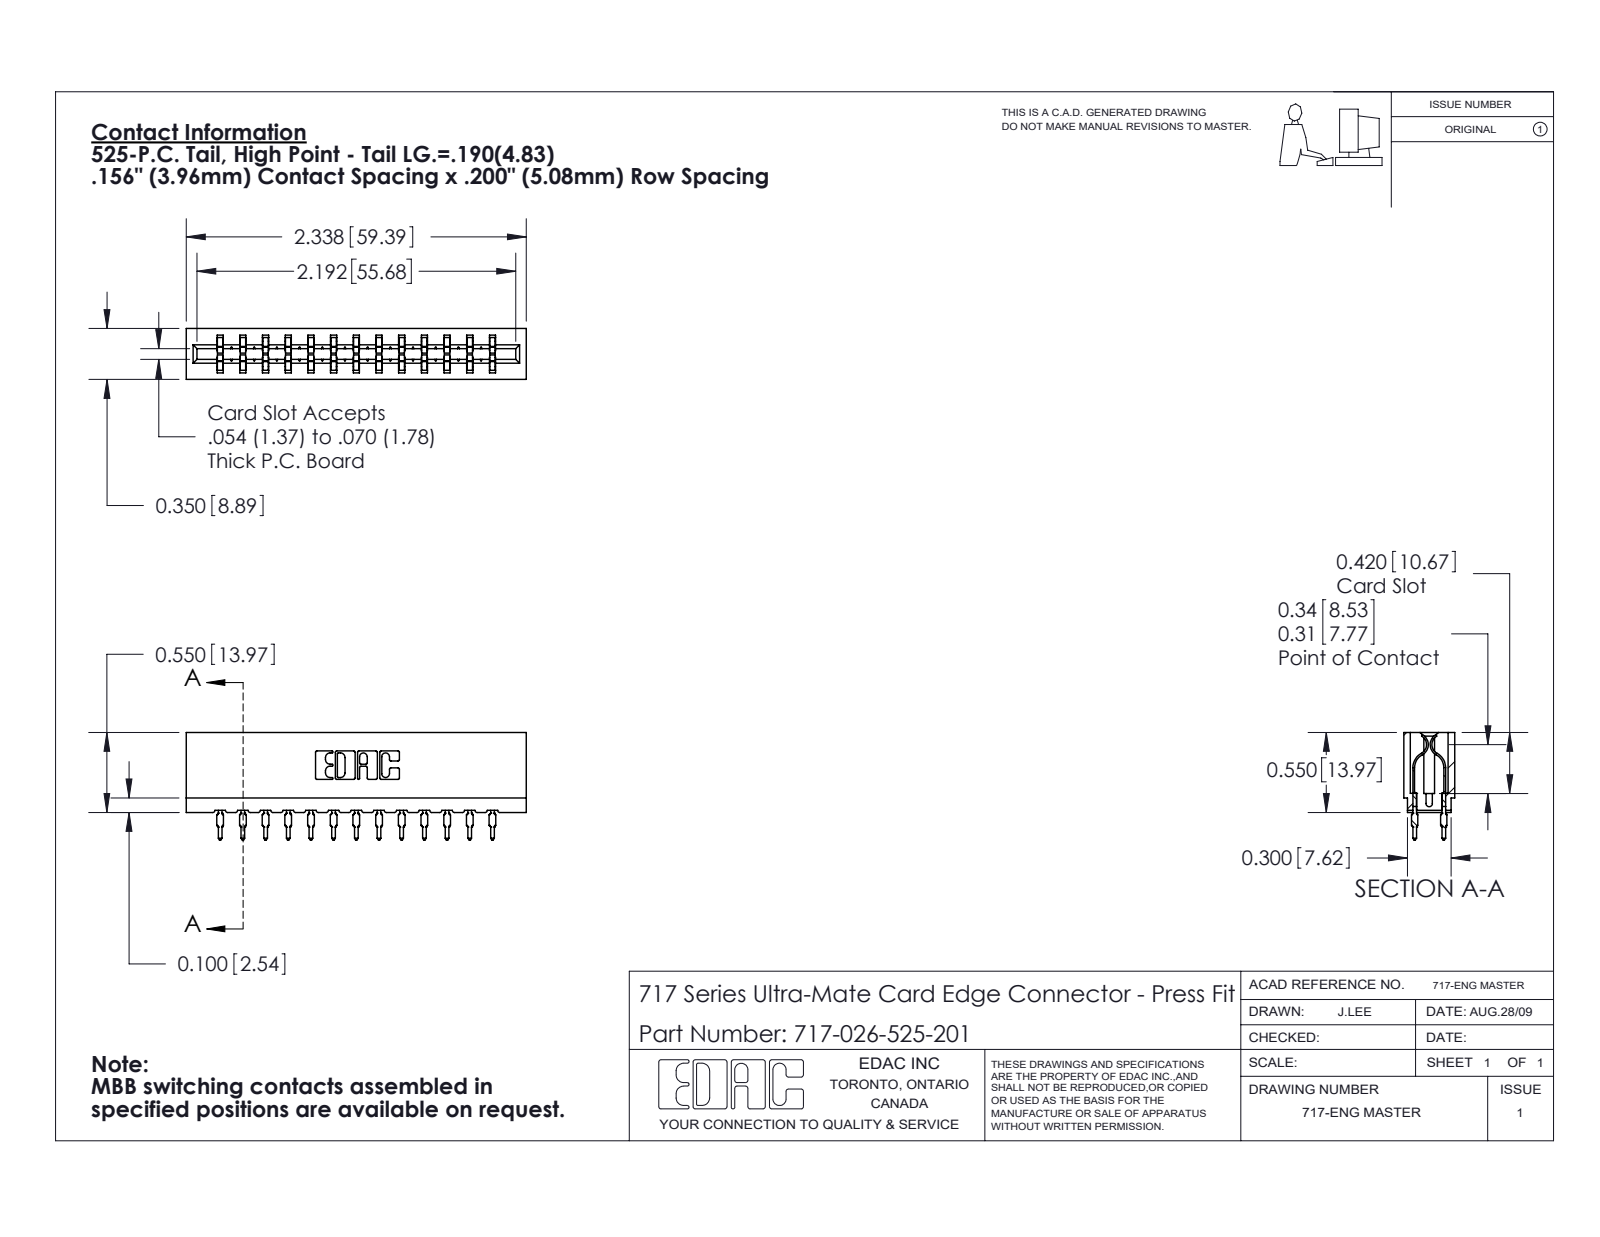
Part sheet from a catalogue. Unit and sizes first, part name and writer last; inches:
Units: inches
Overall size (bounding box): 2.338 × 0.739 × 0.35
Partial cylindrical surfaces — rounded edges, fillets, slot ends (radius × count): R0.021 ×52, R0.015 ×26, R0.01 ×22, R0.005 ×8, R0.011 ×8, R0.007 ×6, R0.031 ×6, R0.026 ×3
Main face-to-face distances: 0.156, 0.212, 0.138, 0.35, 0.624, 0.468, 0.312, 0.198, 0.426, 0.78
Volume: 0.321 in³ · Surface area: 11.82 in²
Bodies: 27 solids, 2434 faces (1263 planar, 495 cylindrical, 676 other)
Part name (STEP PRODUCT): 717 Part_Insulator Option - 06; 745-292-001_525; 717-026-525-201
STEP written by: SolidWorks 2020 (CONFIG_CONTROL_DESIGN)
